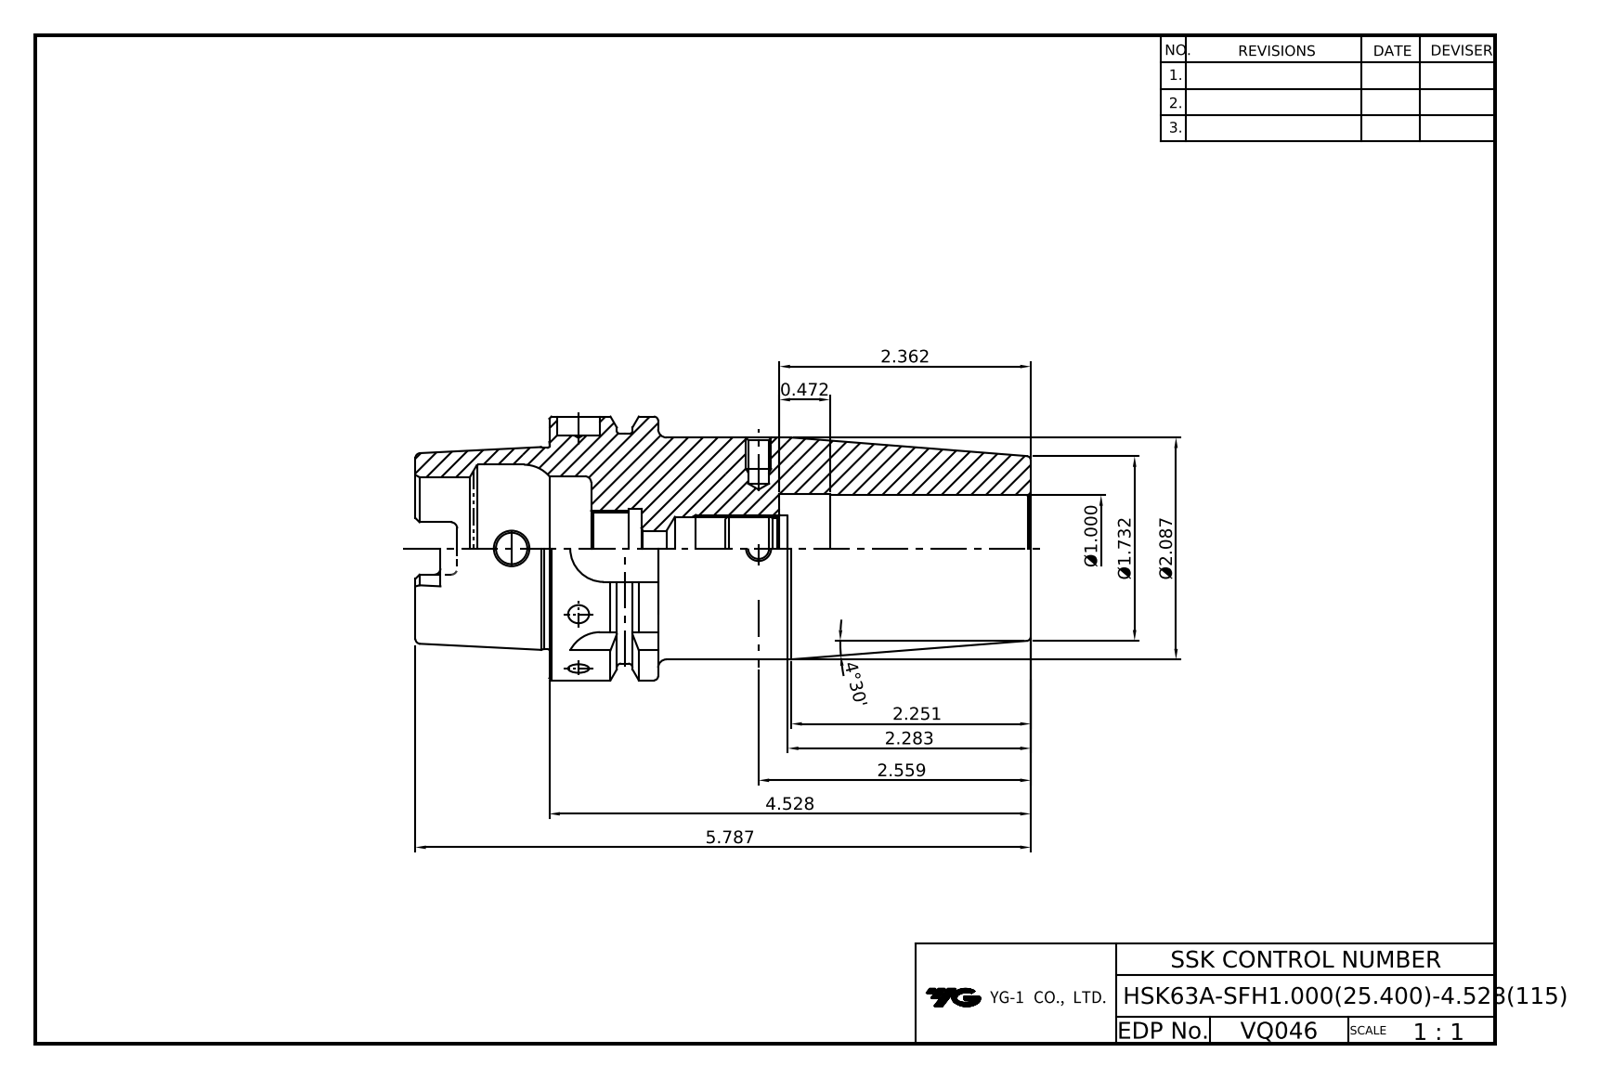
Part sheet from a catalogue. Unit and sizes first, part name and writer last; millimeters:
Units: millimetres
Overall size (bounding box): 147 × 63 × 63
Round holes (diameter × count): ⌀7.5 ×1, ⌀8.4 ×1, ⌀10 ×1, ⌀14.92 ×1, ⌀16.92 ×1, ⌀19 ×1, ⌀25.4 ×1, ⌀26.6 ×1, ⌀34 ×1, ⌀40 ×1
Round bosses / shafts (diameter × count): ⌀63 ×1, ⌀55 ×1, ⌀53 ×1, ⌀48.04 ×1
Partial cylindrical surfaces — rounded edges, fillets, slot ends (radius × count): R1.5 ×6, R2.88 ×4, R8 ×4
Main face-to-face distances: 115, 10, 105, 32, 26, 45, 89, 16, 29, 55
Volume: 222 005 mm³ · Surface area: 41 633 mm²
Bodies: 1 solid, 119 faces (44 planar, 34 cylindrical, 41 other)
Part name (STEP PRODUCT): LO-HSK63A-SFH25.4-115
STEP written by: Autodesk Inventor 2022 (AUTOMOTIVE_DESIGN)
